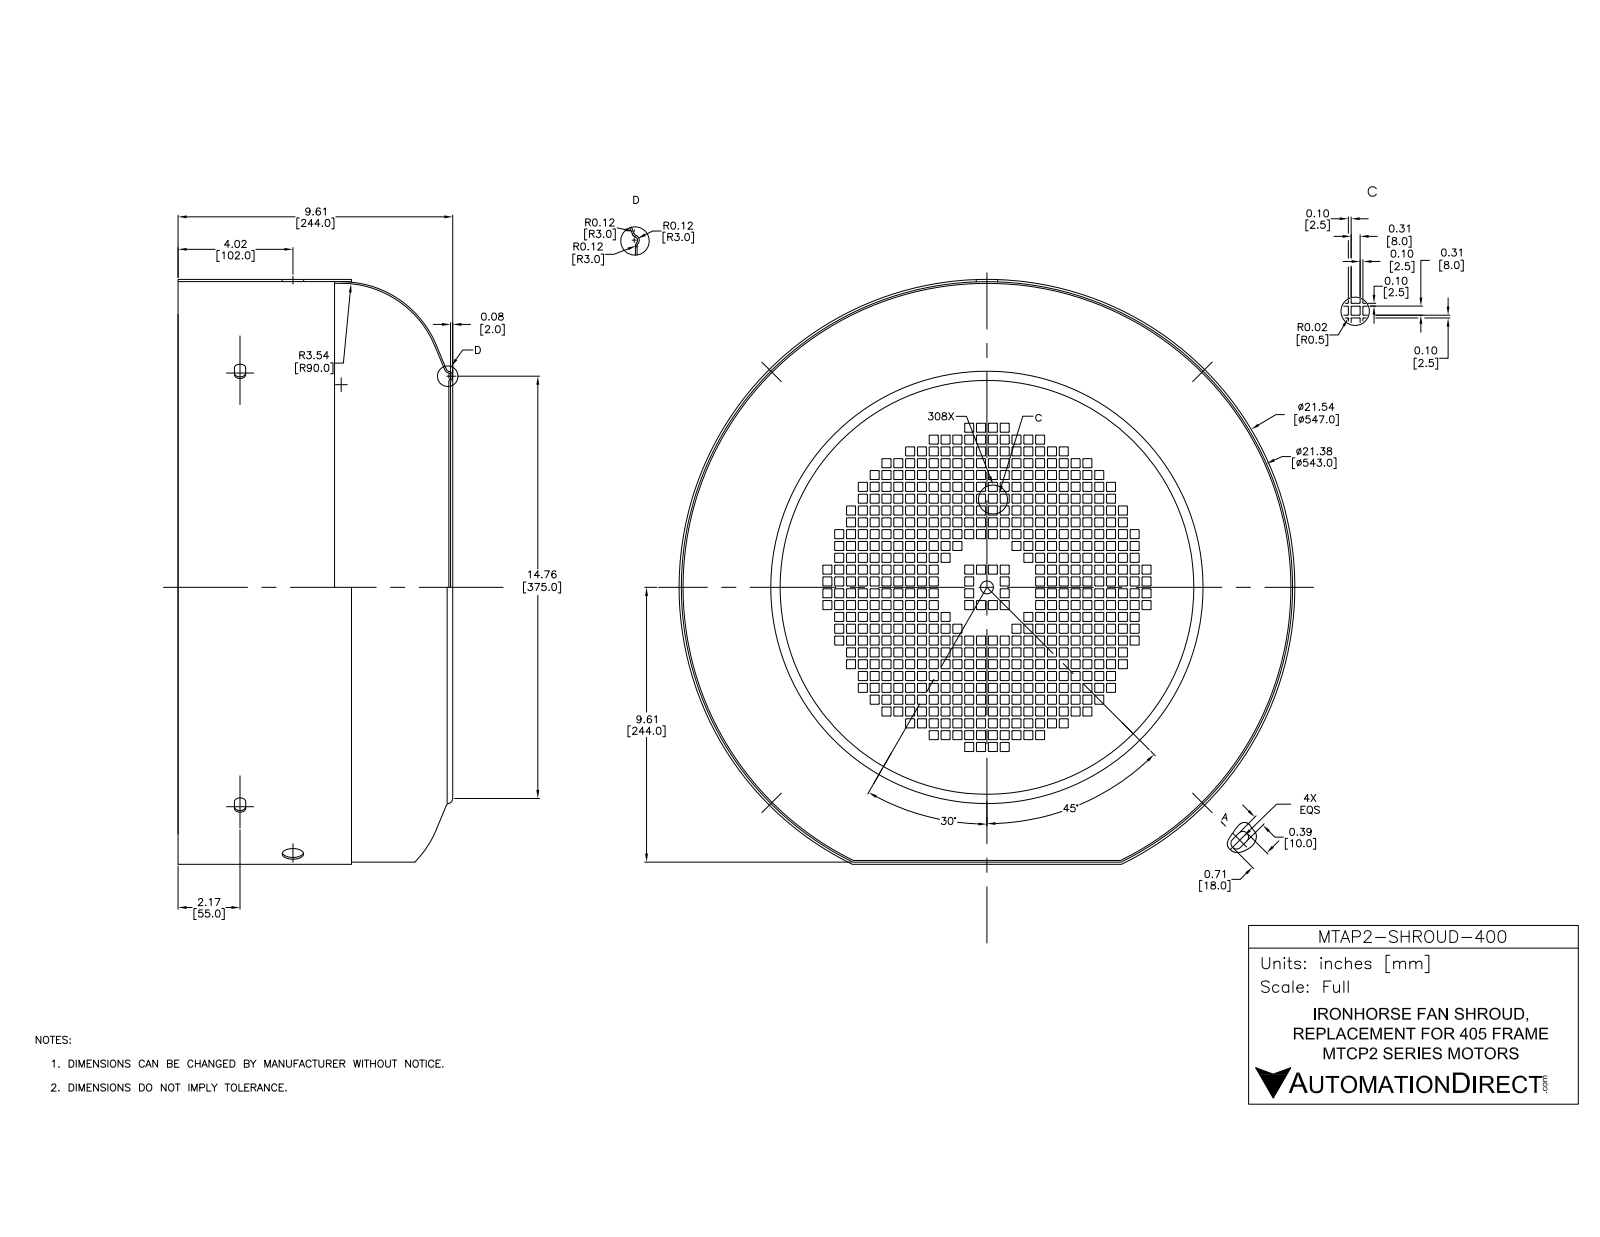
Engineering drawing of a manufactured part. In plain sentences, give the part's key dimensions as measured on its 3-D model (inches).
The part is named "MTAP2-SHROUD-400". Its 3-D file was written by "SolidWorks 2017 (AUTOMOTIVE_DESIGN)". It is 4 solids with 2360 faces: 1286 planar, 1050 cylindrical and 24 other. Overall it measures 21.535 by 21.535 by 9.606 inches. Its volume is 61.68 cubic inches and its surface area 1 869 square inches. Round holes: 2 of diameter 0.748, 1 of diameter 0.453, 1 of diameter 21.26, 1 of diameter 21.378. Round bosses or shafts: 2 of diameter 0.866, 2 of diameter 0.827, 2 of diameter 0.728, 1 of diameter 21.535. Partial cylindrical surfaces (rounded edges, fillets, slot ends): 1008 of radius 0.02, 4 of radius 0.197. The main face-to-face distances are 0.059, 0.079, 0.02, 0.039, 0.08, 0.139, 0.061, 3.406, 3.425, 3.465.
